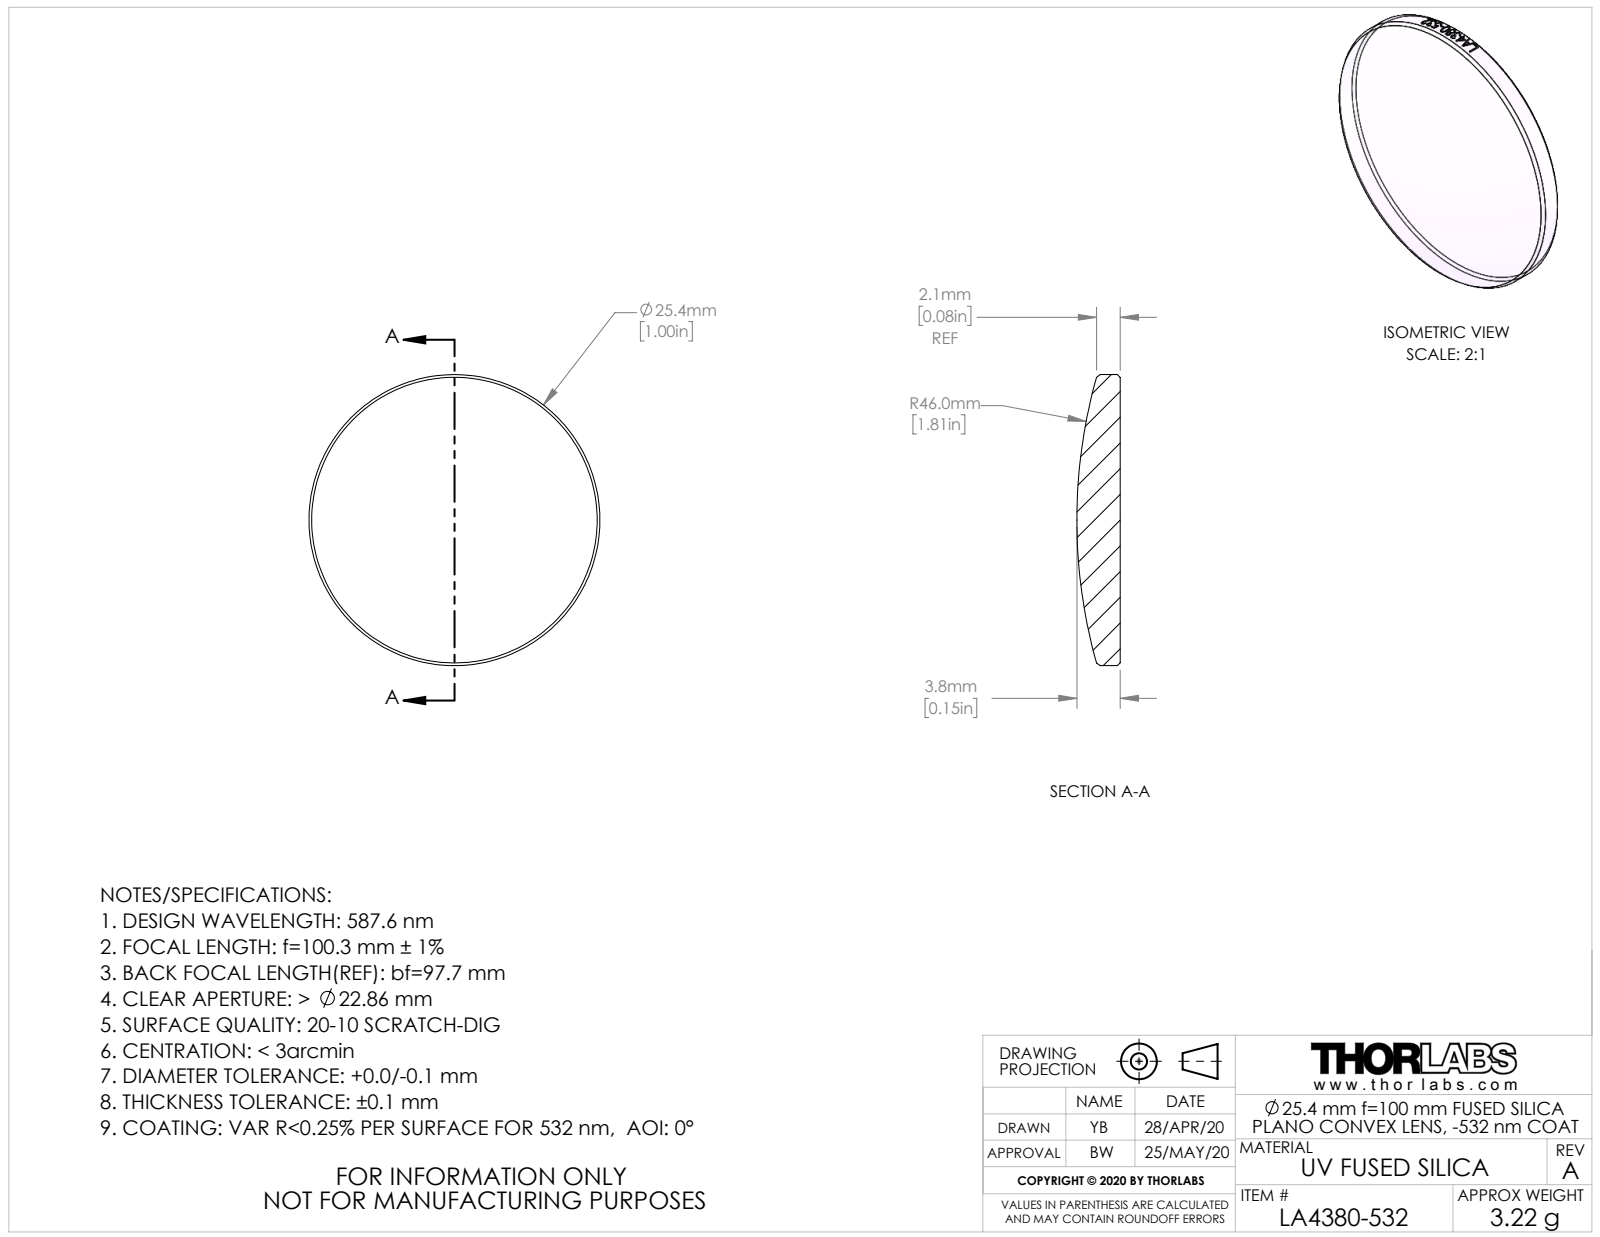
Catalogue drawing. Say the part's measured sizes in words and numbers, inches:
The part is named "CTN015728-E0W". Its 3-D file was written by "SolidWorks 2018 (AUTOMOTIVE_DESIGN)". It is 1 solid with 28 faces: 1 planar, 21 cylindrical and 6 other. Overall it measures 1 by 1 by 0.149 inches. Its volume is 0.089 cubic inches and its surface area 1.803 square inches. Round bosses or shafts: 1 of diameter 1.
